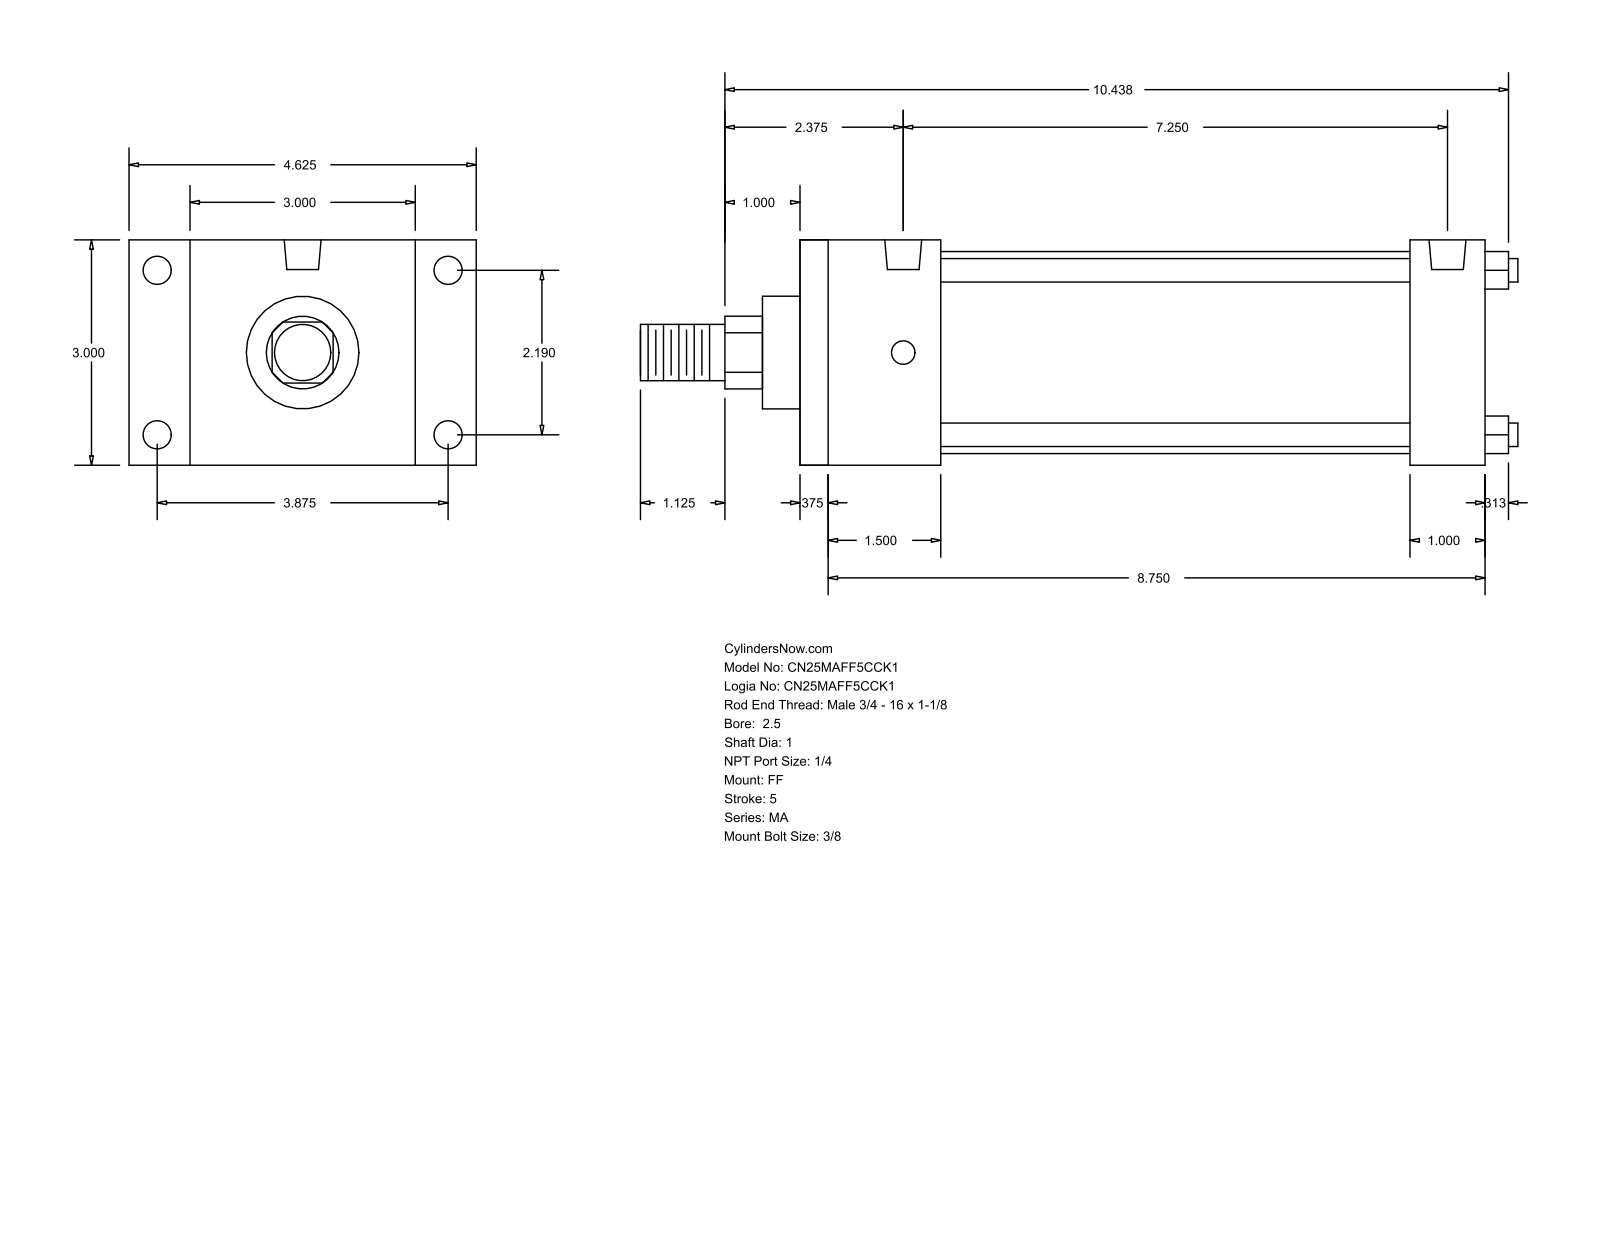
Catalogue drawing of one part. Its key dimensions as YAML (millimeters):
part_name: "MA_FF__0250_1"
step_written_by: "GSSL Pune (CONFIG_CONTROL_DESIGN)"
units: millimeters
bodies: {solids: 0, faces: 92, planar: 64, cylindrical: 28, other: 0}
overall_size: [296.86, 117.47, 76.2]
round_holes:
  - {diameter: 7.94, count: 4}
  - {diameter: 9.53, count: 4}
  - {diameter: 12.49, count: 2}
round_bosses_or_shafts:
  - {diameter: 7.94, count: 4}
  - {diameter: 68.33, count: 1}
  - {diameter: 38.1, count: 1}
  - {diameter: 25.4, count: 1}
  - {diameter: 19.05, count: 1}
partial_cylinders:
  - {radius: 12.29, count: 1}
face_to_face_distances: [76.2, 231.78, 9.52, 222.26, 25.4, 47.63, 206.38, 38.11, 196.86, 158.75]
hole_center_spacings: [55.62, 98.42, 113.05, 184.14]
